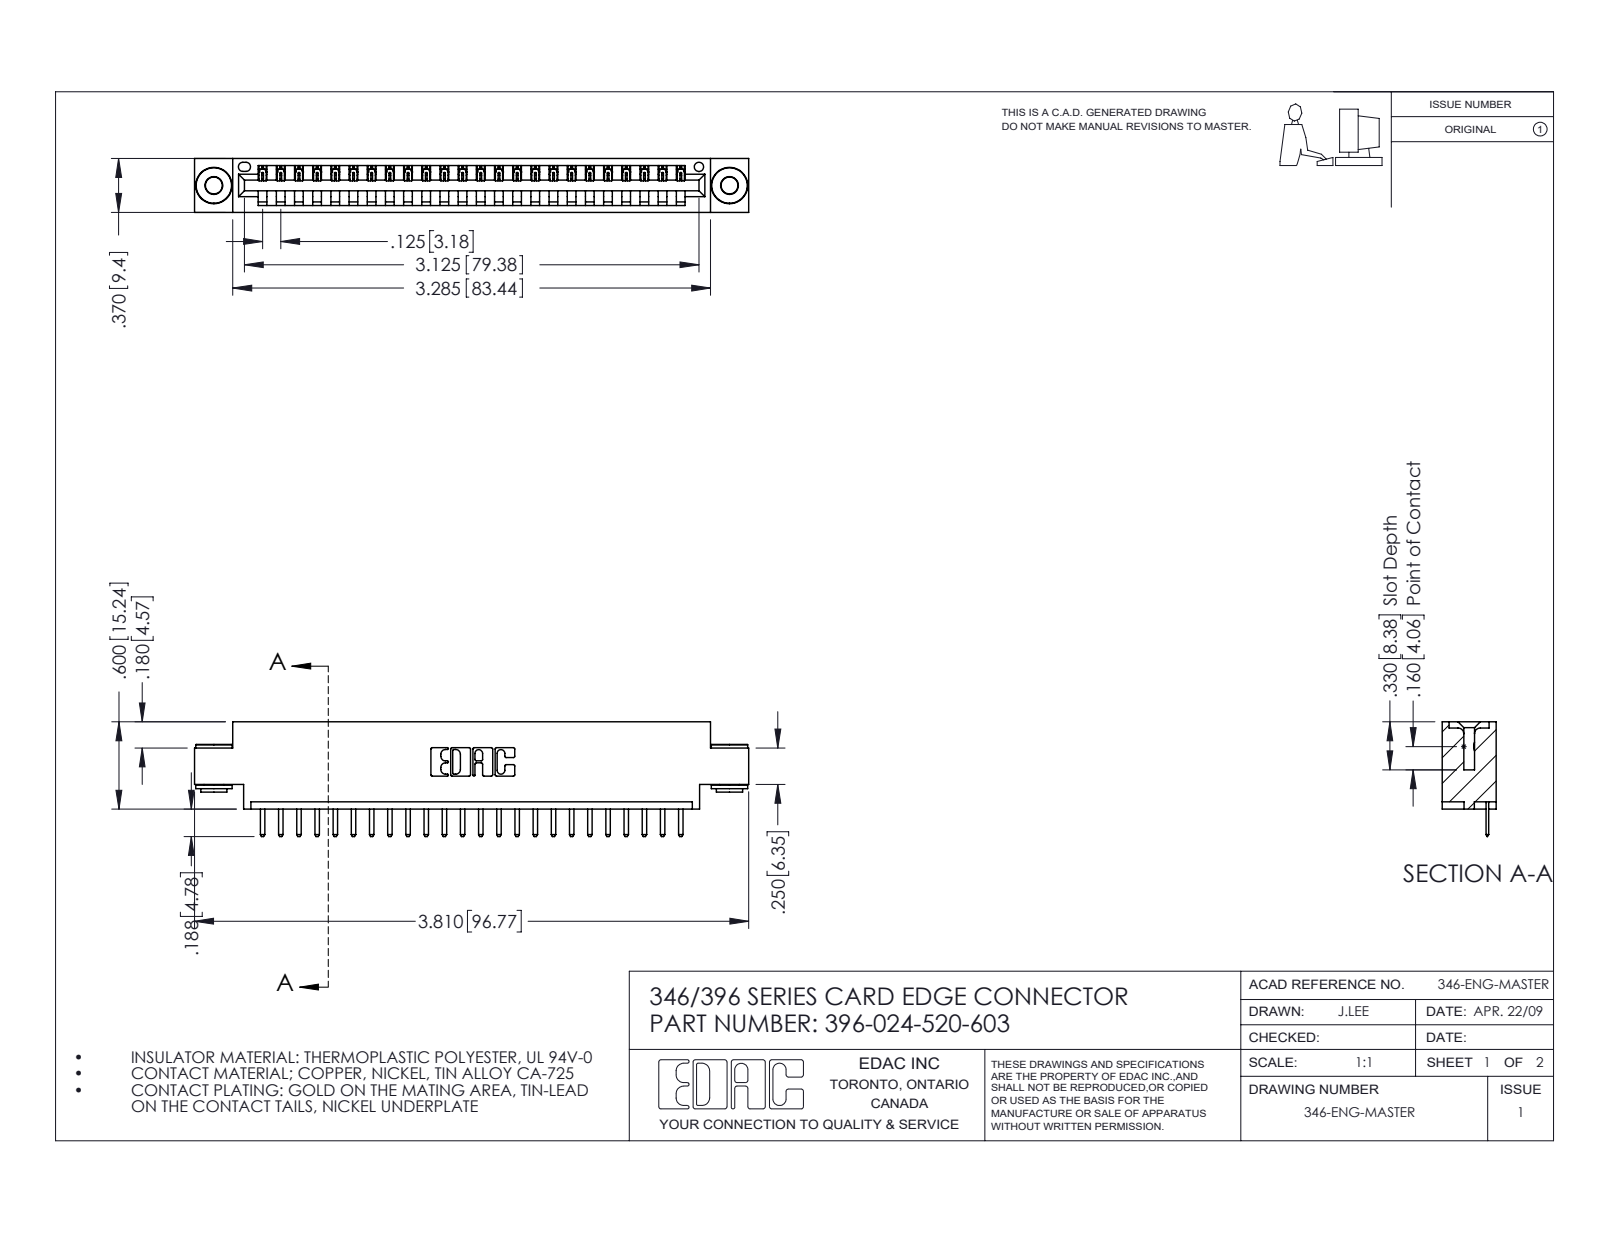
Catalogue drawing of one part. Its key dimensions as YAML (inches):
part_name: "345-250-002_345-250-002-102; 345-292-001_345-293-120; 396-024-520-603; 346 Part_0.170 Offset - 0.156 Dia-TH"
step_written_by: "SolidWorks 2016 (CONFIG_CONTROL_DESIGN)"
units: inches
bodies: {solids: 27, faces: 1652, planar: 1098, cylindrical: 546, other: 8}
overall_size: [3.81, 0.788, 0.37]
volume: 0.545
surface_area: 17.24
round_holes:
  - {diameter: 0.116, count: 2}
  - {diameter: 0.156, count: 2}
  - {diameter: 0.064, count: 1}
round_bosses_or_shafts:
  - {diameter: 0.25, count: 2}
  - {diameter: 0.18, count: 2}
  - {diameter: 0.136, count: 2}
partial_cylinders:
  - {radius: 0.01, count: 50}
  - {radius: 0.006, count: 48}
  - {radius: 0.01, count: 22}
  - {radius: 0.007, count: 6}
  - {radius: 0.031, count: 6}
  - {radius: 0.026, count: 3}
  - {radius: 0.031, count: 2}
  - {radius: 0.04, count: 2}
face_to_face_distances: [0.37, 0.048, 0.322, 0.25, 0.025, 0.148, 0.222, 0.1, 0.174, 0.072]
hole_center_spacings: [0.246, 3.337, 3.545]
